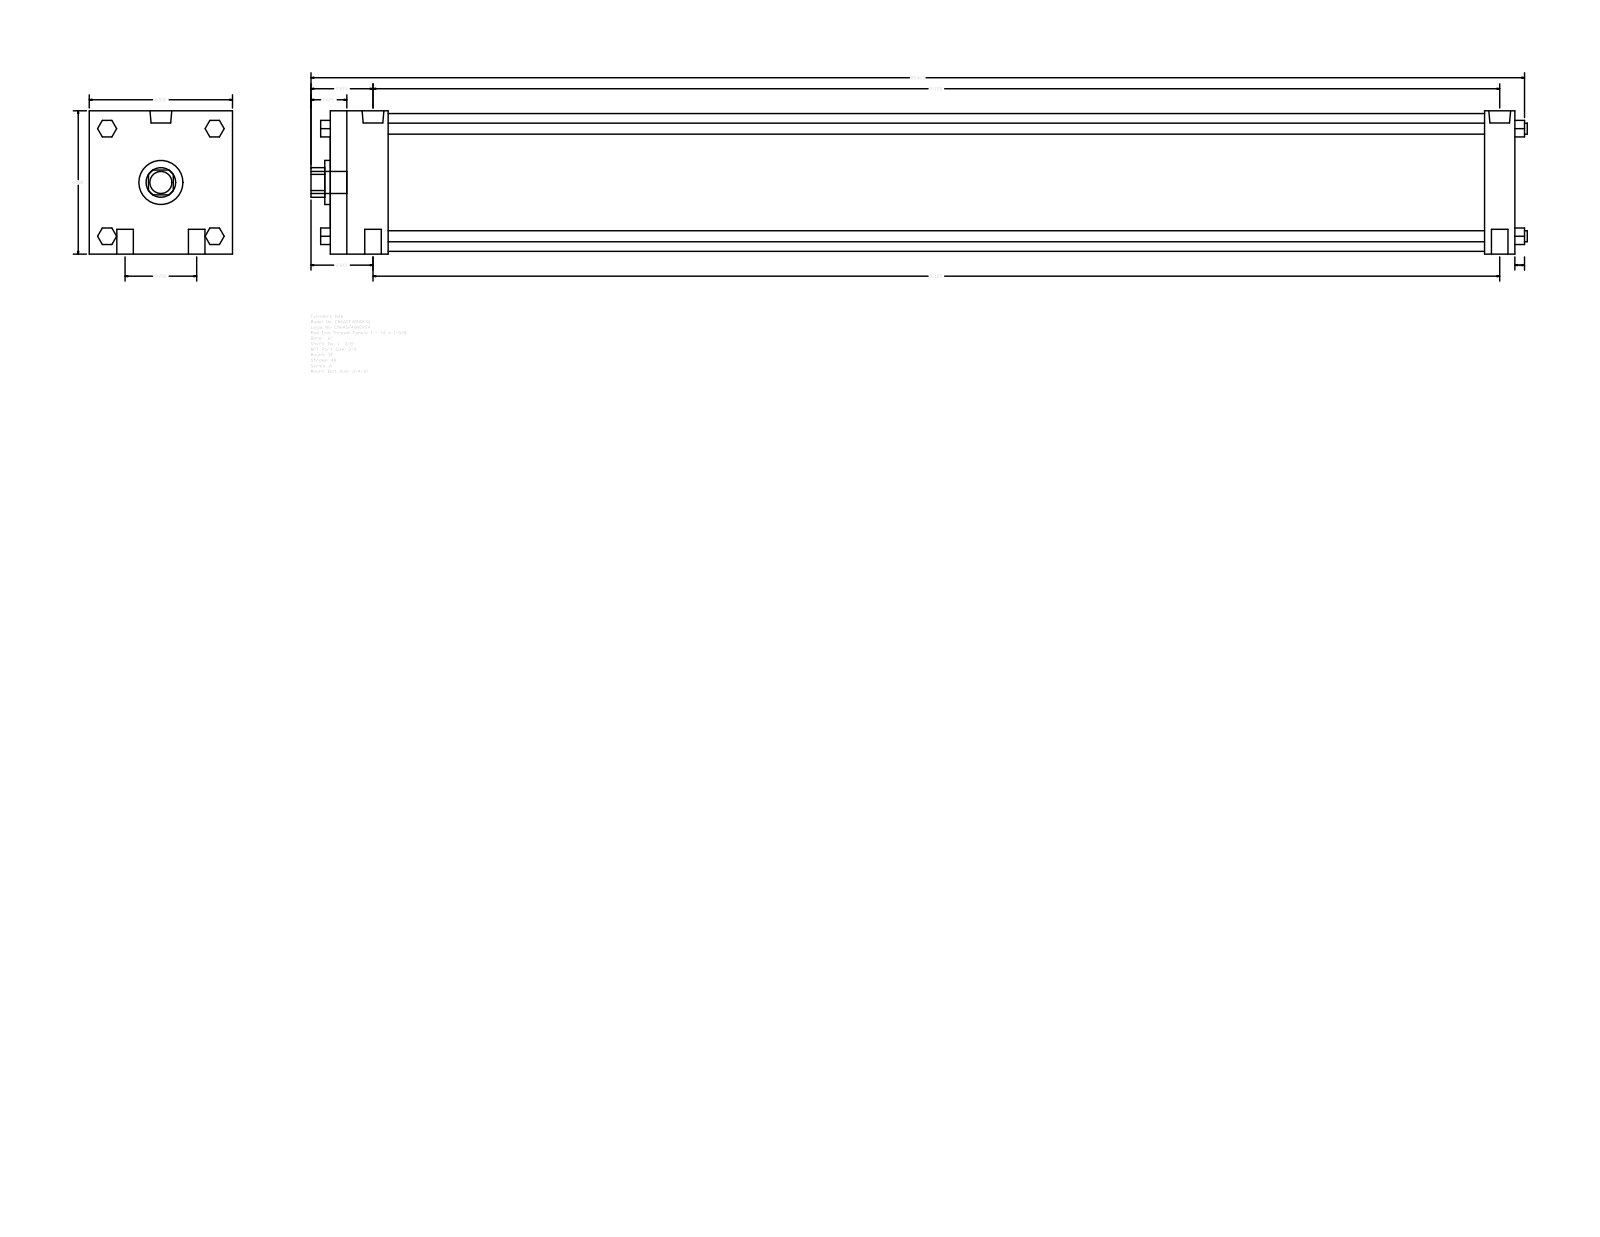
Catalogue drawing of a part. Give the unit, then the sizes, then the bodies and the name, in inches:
Units: inches
Overall size (bounding box): 55.187 × 6.5 × 6.5
Round holes (diameter × count): ⌀1.375 ×1, ⌀2 ×1, ⌀6.25 ×1
Round bosses / shafts (diameter × count): ⌀0.75 ×4, ⌀0.5 ×4, ⌀0.989 ×2, ⌀0.594 ×2, ⌀1 ×1
Partial cylindrical surfaces — rounded edges, fillets, slot ends (radius × count): R0.672 ×1
Main face-to-face distances: 6.5, 53.75, 52.375, 1.375, 2.625, 49.75, 51.125, 0.75, 2.44, 4.226
Bodies: 0 solids, 124 faces (94 planar, 30 cylindrical, 0 other)
Part name (STEP PRODUCT): A_SF__0600_1.375
STEP written by: GSSL Pune (CONFIG_CONTROL_DESIGN)
